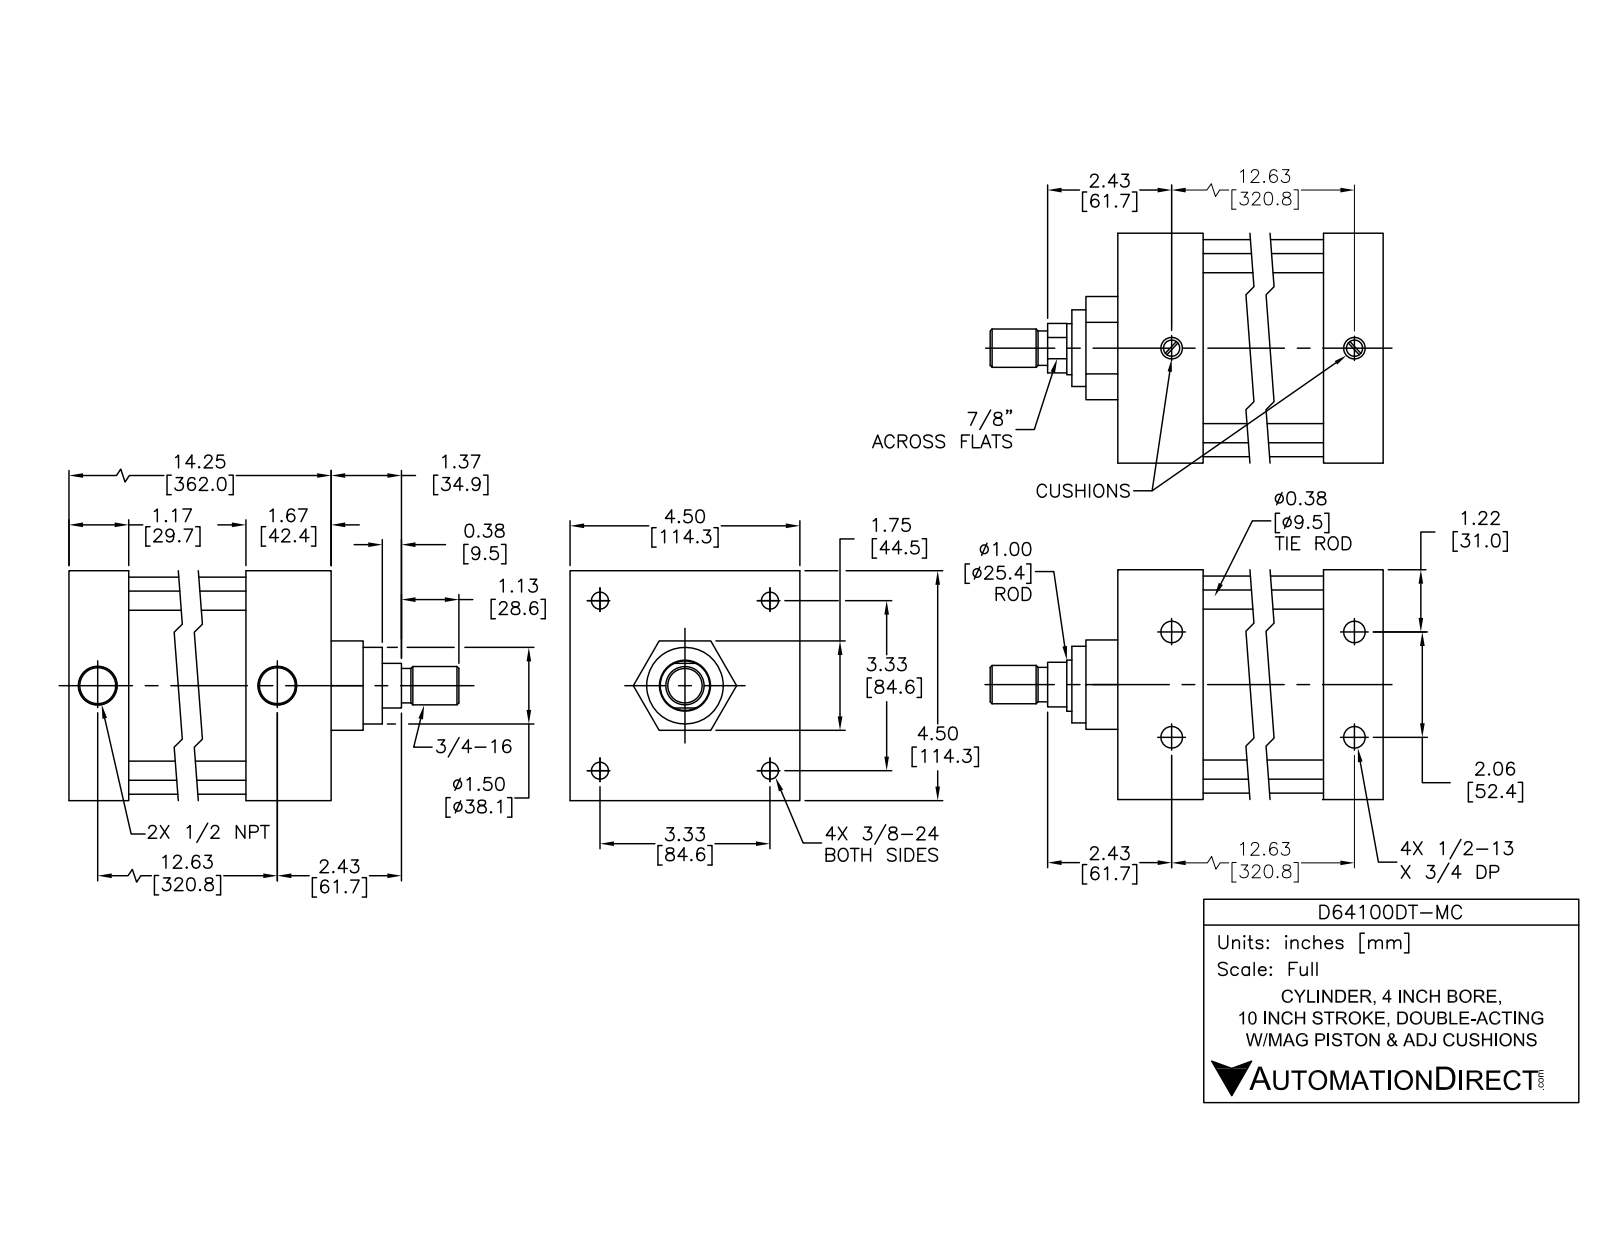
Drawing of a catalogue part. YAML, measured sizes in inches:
part_name: "D64100DT-MC; D64100DT-M BODY; D64100DT-M PISTON"
step_written_by: "SolidWorks 2015 (AUTOMOTIVE_DESIGN)"
units: inches
bodies: {solids: 12, faces: 303, planar: 99, cylindrical: 114, other: 90}
overall_size: [16.745, 4.5, 4.5]
volume: 105
surface_area: 623.6
round_holes:
  - {diameter: 0.33, count: 4}
  - {diameter: 0.406, count: 4}
  - {diameter: 0.417, count: 4}
  - {diameter: 0.625, count: 4}
  - {diameter: 0.5, count: 2}
  - {diameter: 0.766, count: 2}
  - {diameter: 1, count: 1}
  - {diameter: 1.003, count: 1}
  - {diameter: 4, count: 1}
round_bosses_or_shafts:
  - {diameter: 0.609, count: 4}
  - {diameter: 0.375, count: 4}
  - {diameter: 0.34, count: 4}
  - {diameter: 4.25, count: 1}
  - {diameter: 3.997, count: 1}
  - {diameter: 1.75, count: 1}
  - {diameter: 0.997, count: 1}
  - {diameter: 0.97, count: 1}
partial_cylinders:
  - {radius: 0.45, count: 4}
face_to_face_distances: [4.5, 0.08, 11.326, 14.246, 1.75, 12.997, 1.249, 11.751, 1.246, 2.495]
hole_center_spacings: [1.031, 12.664, 12.622, 2.062, 2.349, 2.349, 3.322, 3.322]
